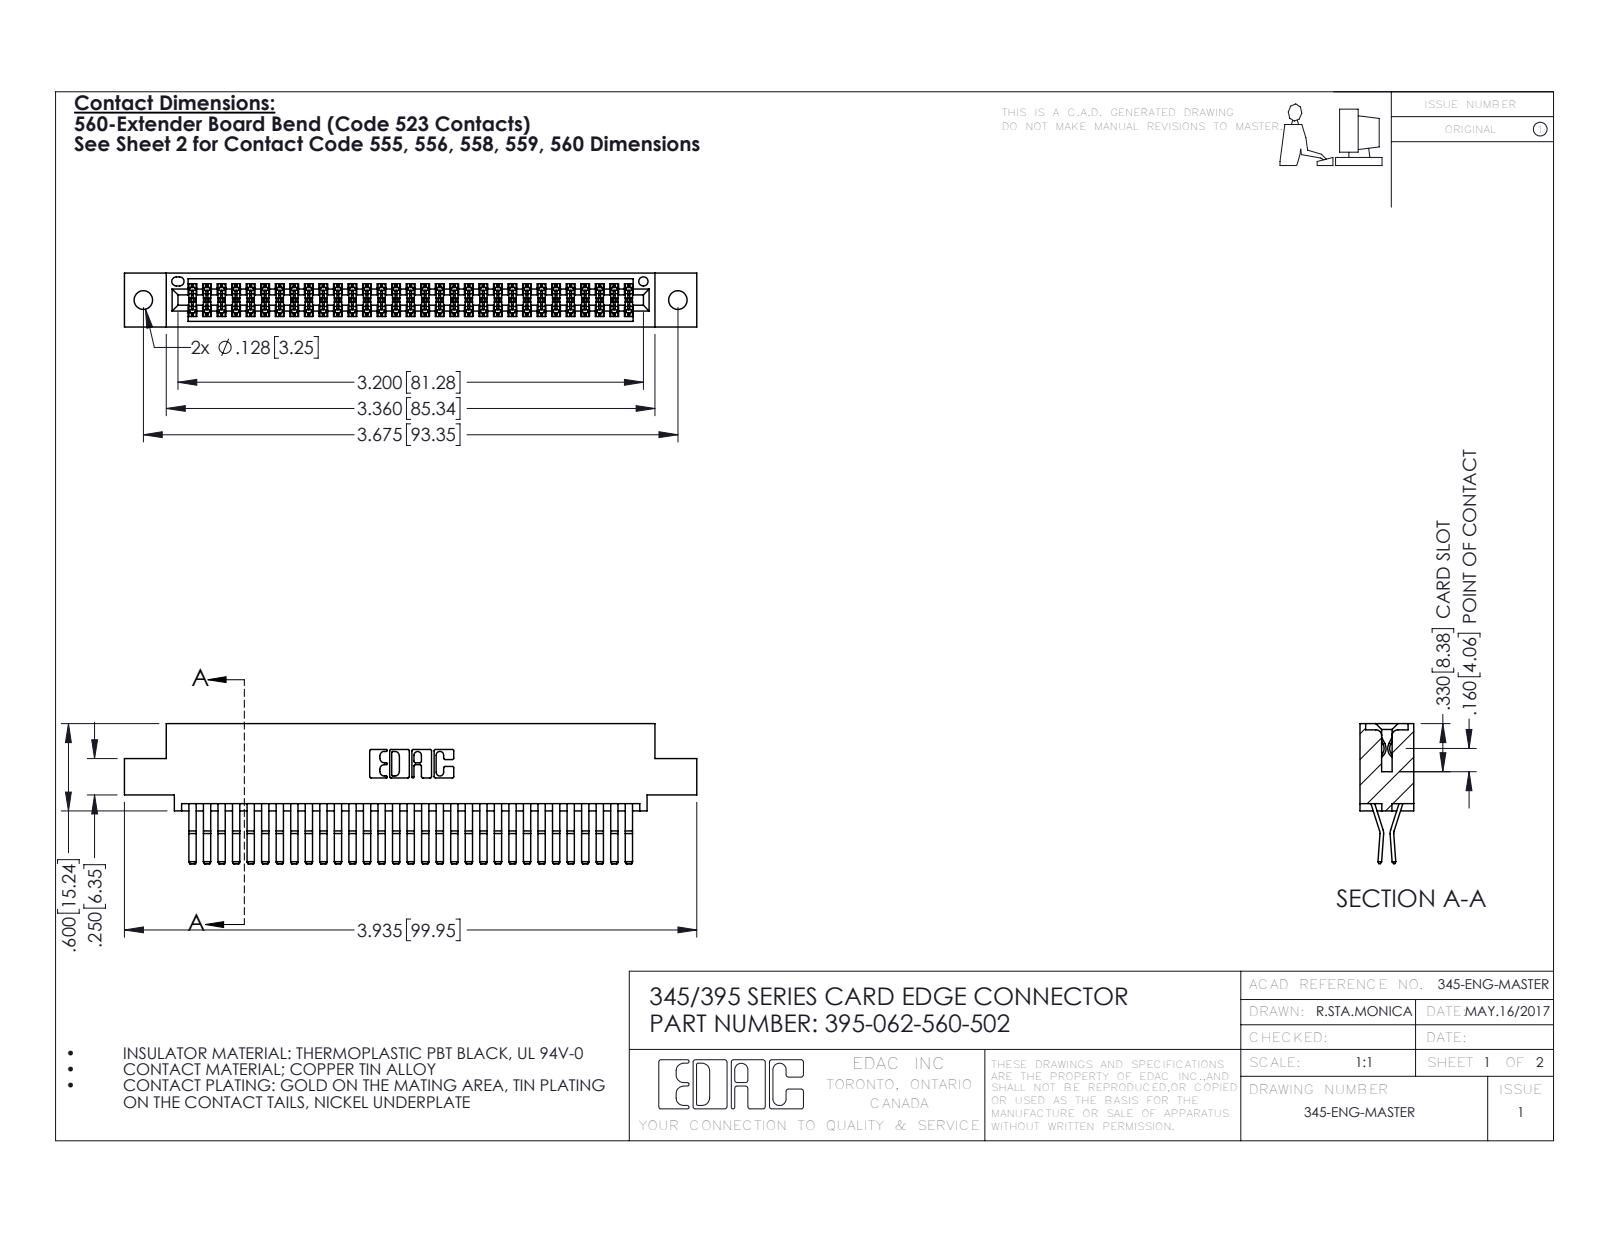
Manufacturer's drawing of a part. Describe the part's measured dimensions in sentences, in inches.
The part is named "345 Part_0.110 Offset - 0.128 Dia; 395-062-560-502; 345-292-001_560 Tail". Its 3-D file was written by "SolidWorks 2016 (CONFIG_CONTROL_DESIGN)". It is 63 solids with 3354 faces: 2130 planar, 1224 cylindrical and 0 other. Overall it measures 3.935 by 0.962 by 0.37 inches. Its volume is 0.604 cubic inches and its surface area 23.7 square inches. Round holes: 2 of diameter 0.128, 1 of diameter 0.064. Partial cylindrical surfaces (rounded edges, fillets, slot ends): 94 of radius 0.006, 22 of radius 0.01, 6 of radius 0.007, 6 of radius 0.031, 3 of radius 0.026, 2 of radius 0.01, 2 of radius 0.014, 2 of radius 0.019. The main face-to-face distances are 0.025, 0.298, 0.072, 0.2, 0.37, 0.098, 0.272, 0.225, 0.175, 0.149. The hole center spacings are 0.27, 3.44, 3.675.
